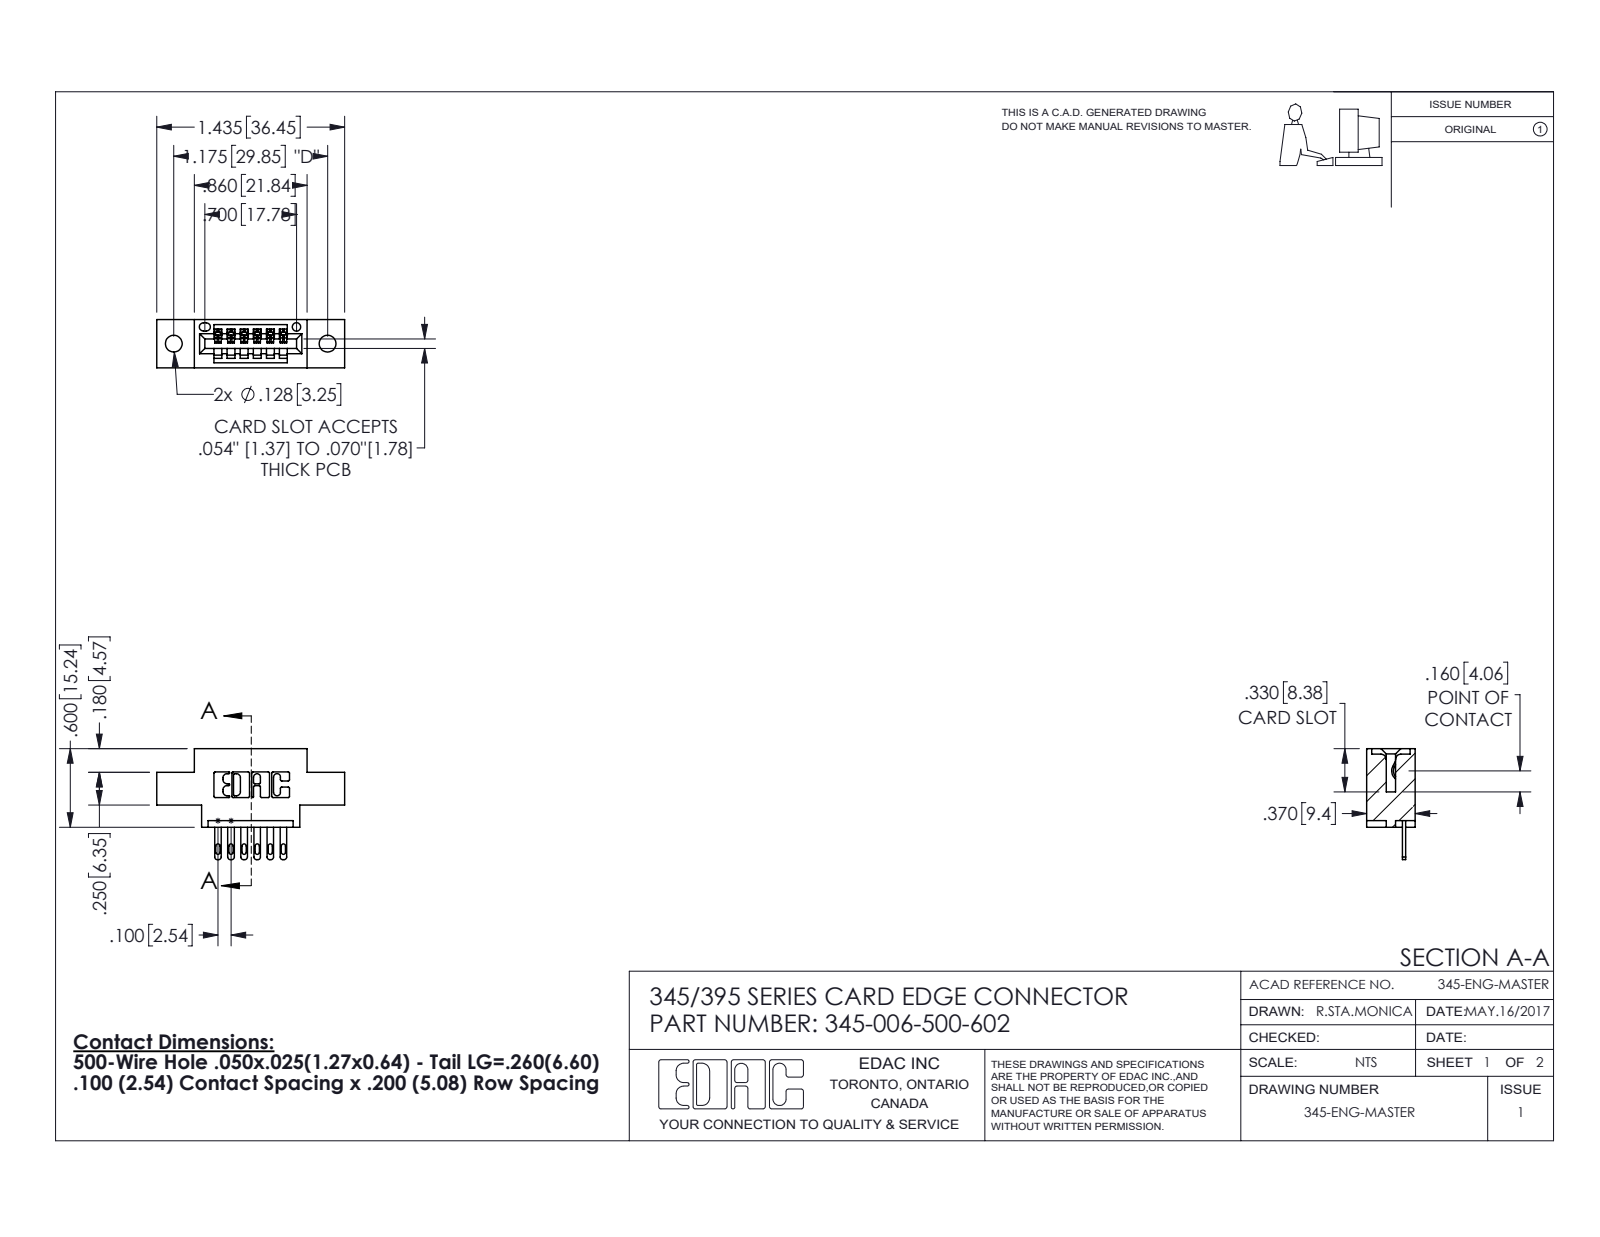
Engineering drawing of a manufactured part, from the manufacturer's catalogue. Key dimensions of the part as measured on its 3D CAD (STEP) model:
Part name (STEP PRODUCT): 345-006-500-602; 345 Part_0.170 Offset - 0.128 Dia; 345-292-001_345-293-100
STEP written by: SolidWorks 2016 (CONFIG_CONTROL_DESIGN)
Units: inches
Bodies: 7 solids, 454 faces (288 planar, 166 cylindrical, 0 other)
Overall size (bounding box): 1.435 × 0.847 × 0.37
Volume: 0.184 in³ · Surface area: 5.26 in²
Round holes (diameter × count): ⌀0.128 ×2, ⌀0.064 ×1
Partial cylindrical surfaces — rounded edges, fillets, slot ends (radius × count): R0.01 ×22, R0.006 ×12, R0.016 ×12, R0.02 ×12, R0.007 ×6, R0.031 ×6, R0.026 ×3, R0.031 ×2
Main face-to-face distances: 0.37, 0.2, 0.298, 0.072, 0.1, 0.025, 0.098, 0.272, 0.06, 0.3
Hole centre spacings: 0.27, 0.946, 1.175
